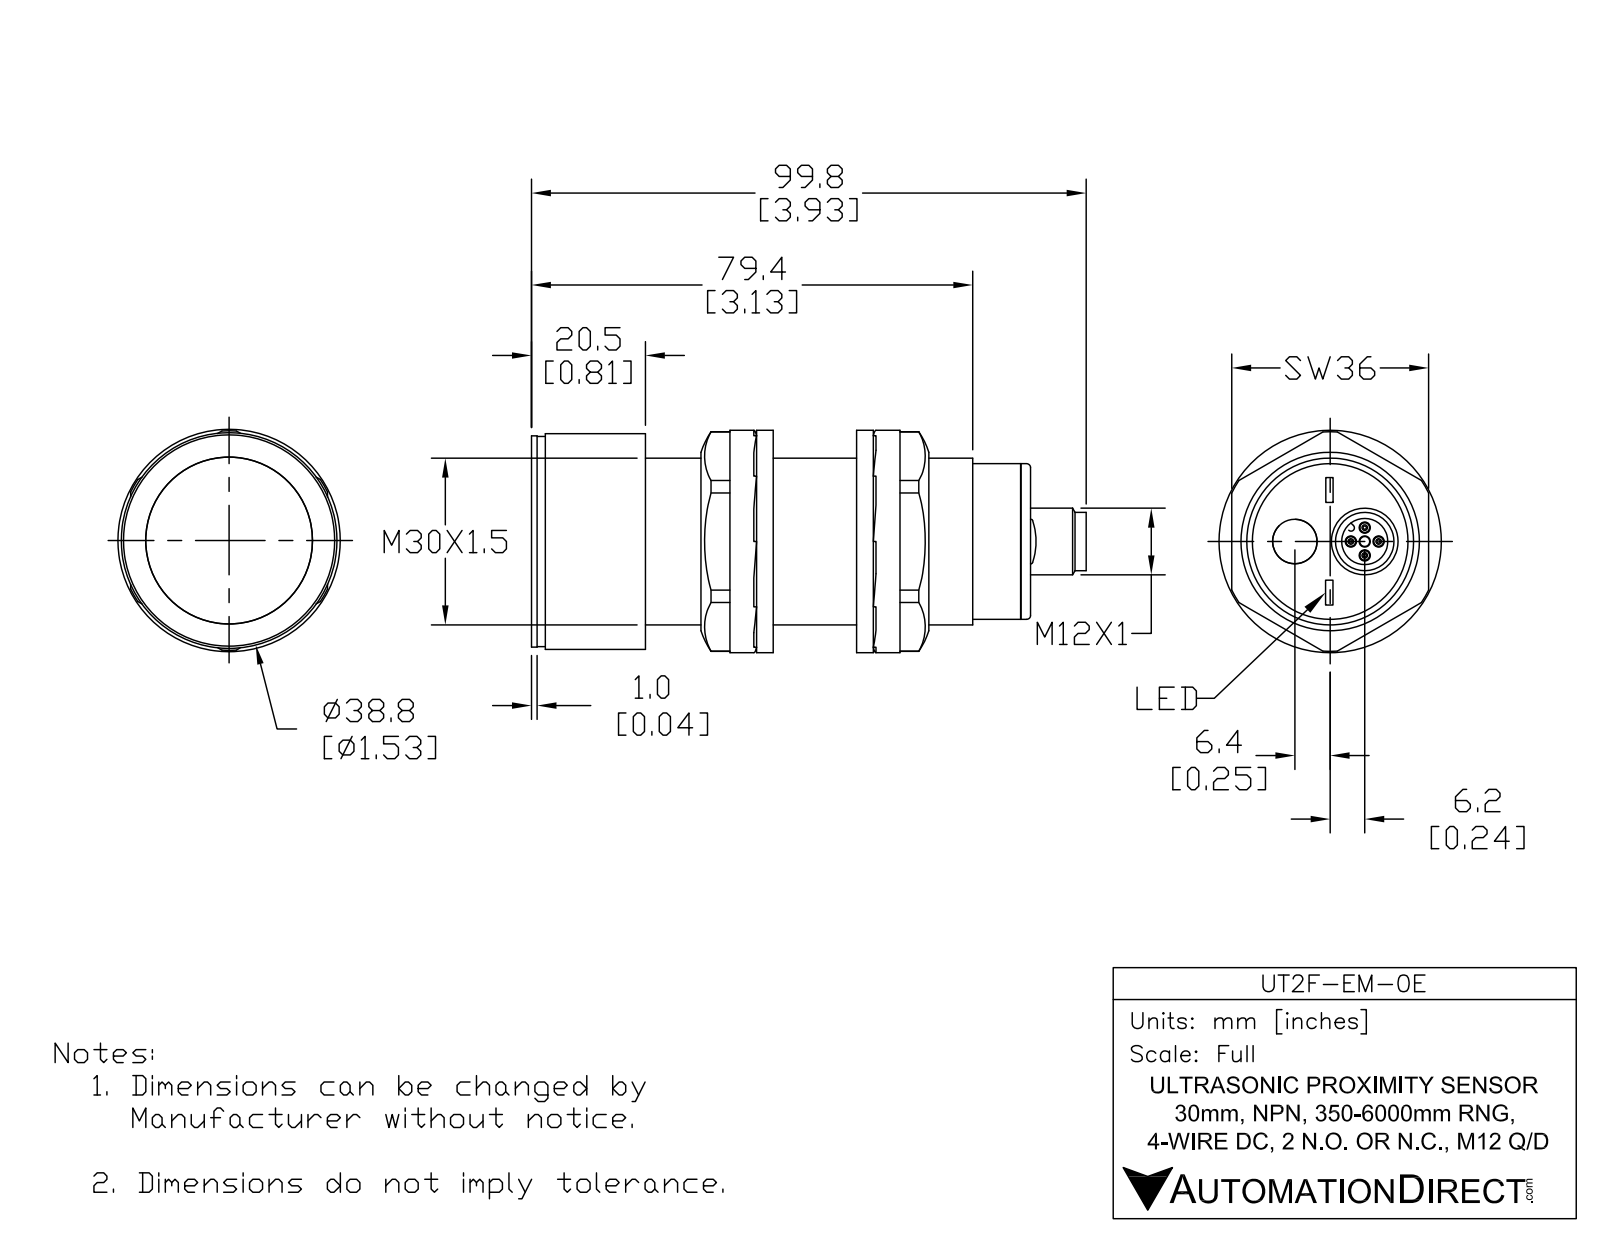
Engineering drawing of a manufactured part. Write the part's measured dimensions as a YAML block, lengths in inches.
part_name: "UT2F-EM-0E"
step_written_by: "SolidWorks 2017 (AUTOMOTIVE_DESIGN)"
units: inches
bodies: {solids: 5, faces: 108, planar: 31, cylindrical: 47, other: 30}
overall_size: [3.894, 1.528, 1.528]
volume: 4.372
surface_area: 24.88
round_holes:
  - {diameter: 0.071, count: 4}
  - {diameter: 0.315, count: 1}
  - {diameter: 0.327, count: 1}
  - {diameter: 0.372, count: 1}
  - {diameter: 1.299, count: 1}
round_bosses_or_shafts:
  - {diameter: 0.039, count: 4}
  - {diameter: 1.528, count: 1}
  - {diameter: 1.488, count: 1}
  - {diameter: 1.181, count: 1}
  - {diameter: 1.102, count: 1}
  - {diameter: 0.472, count: 1}
  - {diameter: 0.413, count: 1}
  - {diameter: 0.364, count: 1}
partial_cylinders:
  - {radius: 0.012, count: 2}
  - {radius: 0.024, count: 1}
face_to_face_distances: [3.37, 0.059, 3.429, 0.767, 0.709, 2.661, 0.059, 3.429, 0.071, 3.5]
hole_center_spacings: [0.098, 0.139, 0.197, 0.264, 0.505, 0.146, 0.245, 0.25]
